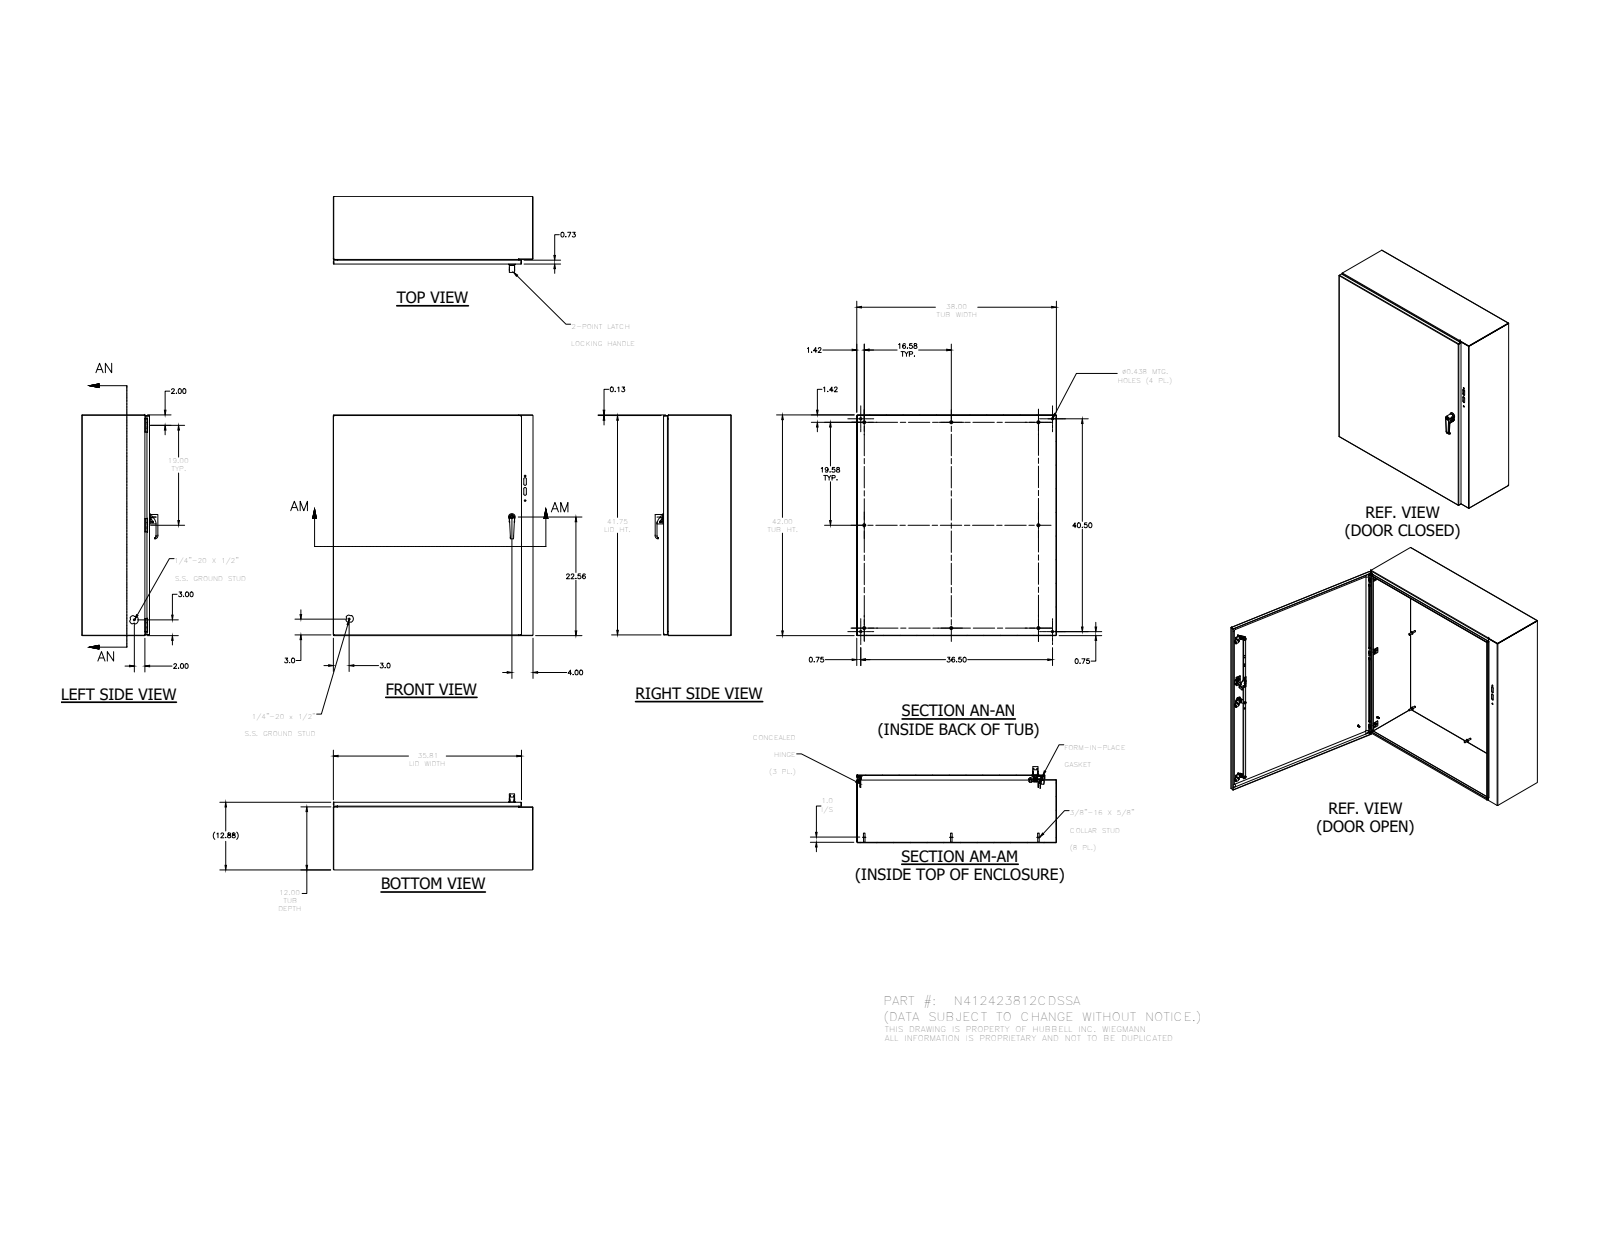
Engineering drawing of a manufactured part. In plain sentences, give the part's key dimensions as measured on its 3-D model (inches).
The part is named "N412423812CDSSA". Its 3-D file was written by "SolidWorks 2019 (AUTOMOTIVE_DESIGN)". It is 84 solids with 2658 faces: 1028 planar, 962 cylindrical and 668 other. Overall it measures 42 by 38 by 14.472 inches. Its volume is 435.2 cubic inches and its surface area 11 257 square inches. Round holes: 6 of diameter 0.093, 6 of diameter 0.145, 6 of diameter 0.152, 6 of diameter 0.167, 6 of diameter 0.172, 6 of diameter 0.187, 5 of diameter 0.156, 4 of diameter 0.32, 4 of diameter 0.437, 3 of diameter 0.196, 3 of diameter 0.211, 3 of diameter 0.22. Round bosses or shafts: 14 of diameter 0.3, 14 of diameter 0.25, 8 of diameter 0.563, 6 of diameter 0.437, 6 of diameter 0.36, 6 of diameter 0.32, 6 of diameter 0.256, 6 of diameter 0.164. Partial cylindrical surfaces (rounded edges, fillets, slot ends): 38 of radius 0.02, 38 of radius 0.05, 34 of radius 0.125, 30 of radius 0.012, 28 of radius 0.031, 26 of radius 0.016, 24 of radius 0.025, 14 of radius 0.105. The main face-to-face distances are 0.074, 12.803, 12.729, 12.877, 37.926, 41.926, 37.852, 38, 41.852, 42. The hole center spacings are 19, 0.5, 38, 19.007, 0.66, 1.307, 1.965, 6.594.
